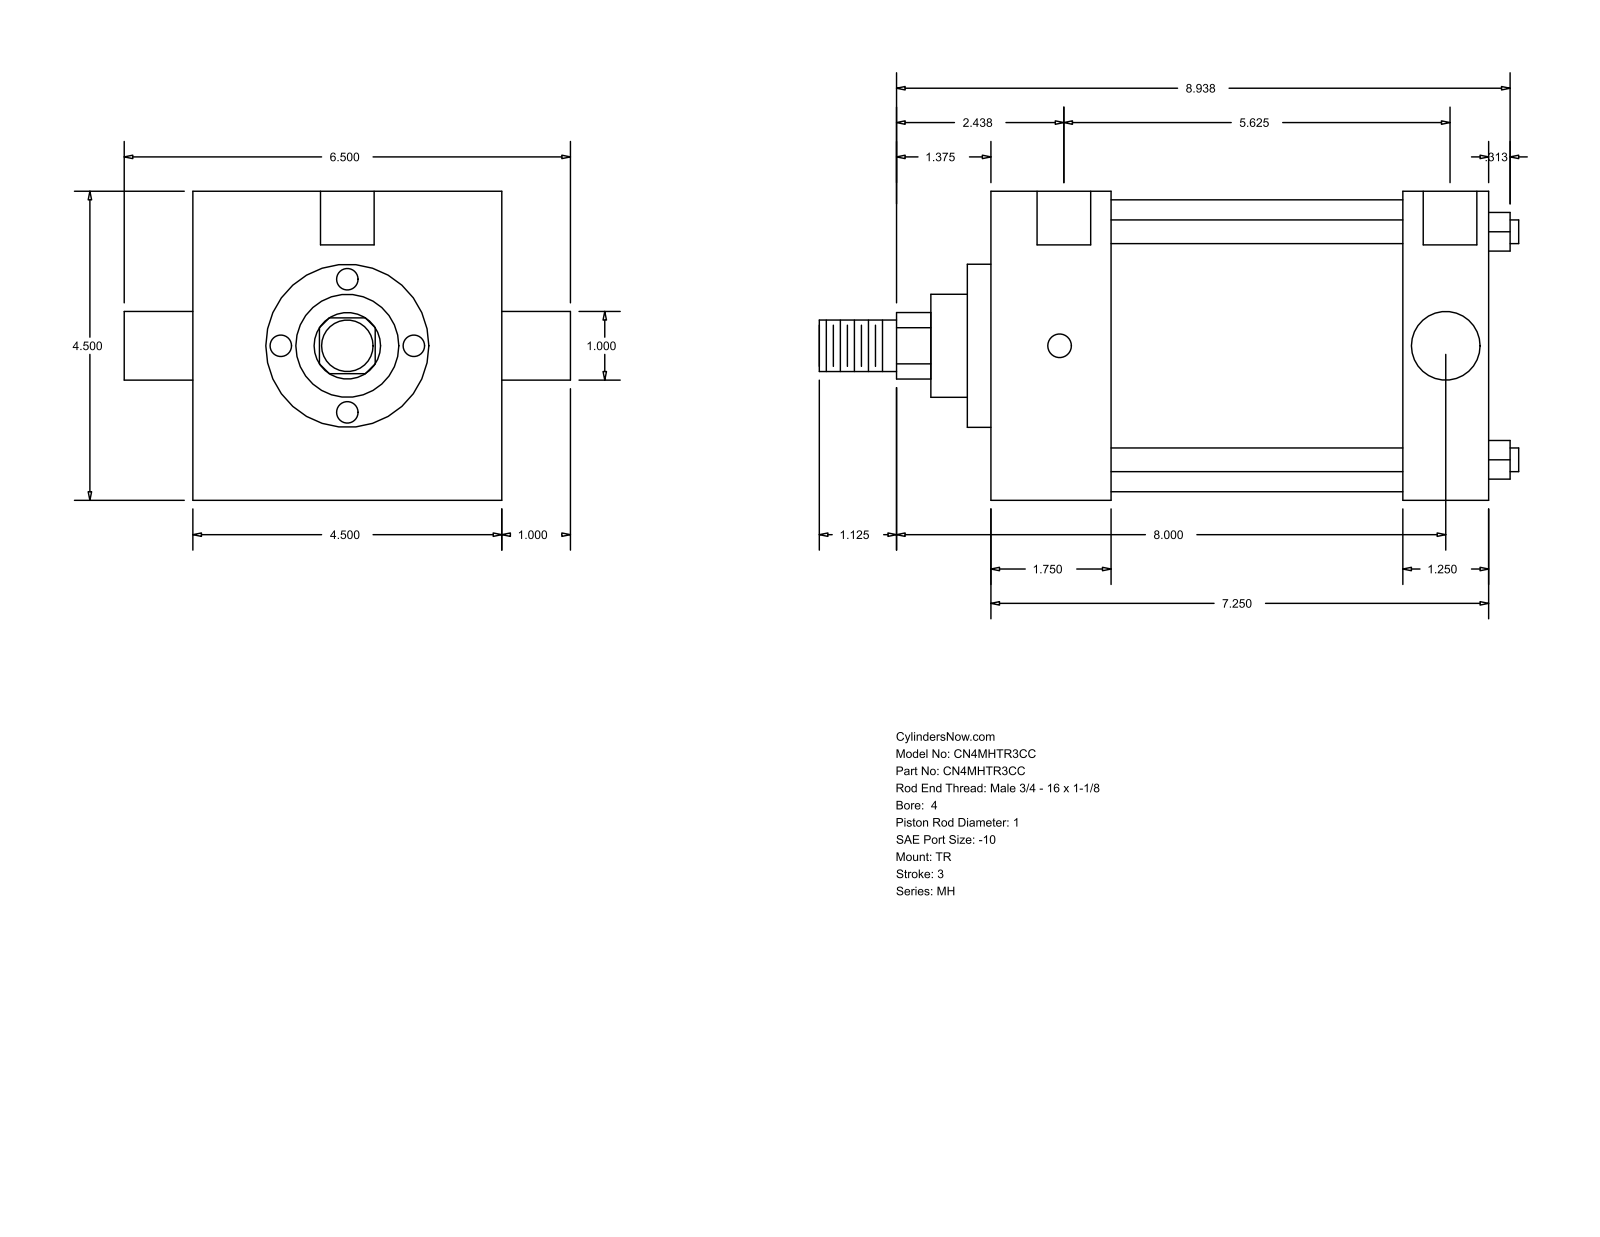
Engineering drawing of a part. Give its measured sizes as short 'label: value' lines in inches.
name: MH_TR__0400_1
written by: GSSL Pune (CONFIG_CONTROL_DESIGN)
unit: in
bodies: 0 solids, 86 faces (61 planar, 25 cylindrical, 0 other)
size: 10.187 × 6.5 × 4.5
holes: 3× ⌀0.344, 2× ⌀0.781
bosses: 4× ⌀0.345, 2× ⌀1, 1× ⌀4.25, 1× ⌀2.375, 1× ⌀1.5, 1× ⌀0.75
rounds: 1× R0.484
face distances: 4.5, 7.25, 1.75, 5.5, 6, 4.25, 1.25, 0.344, 2.094, 6.344
hole spacings: 0.062, 0.063, 5.625, 5.687, 5.688, 5.75
